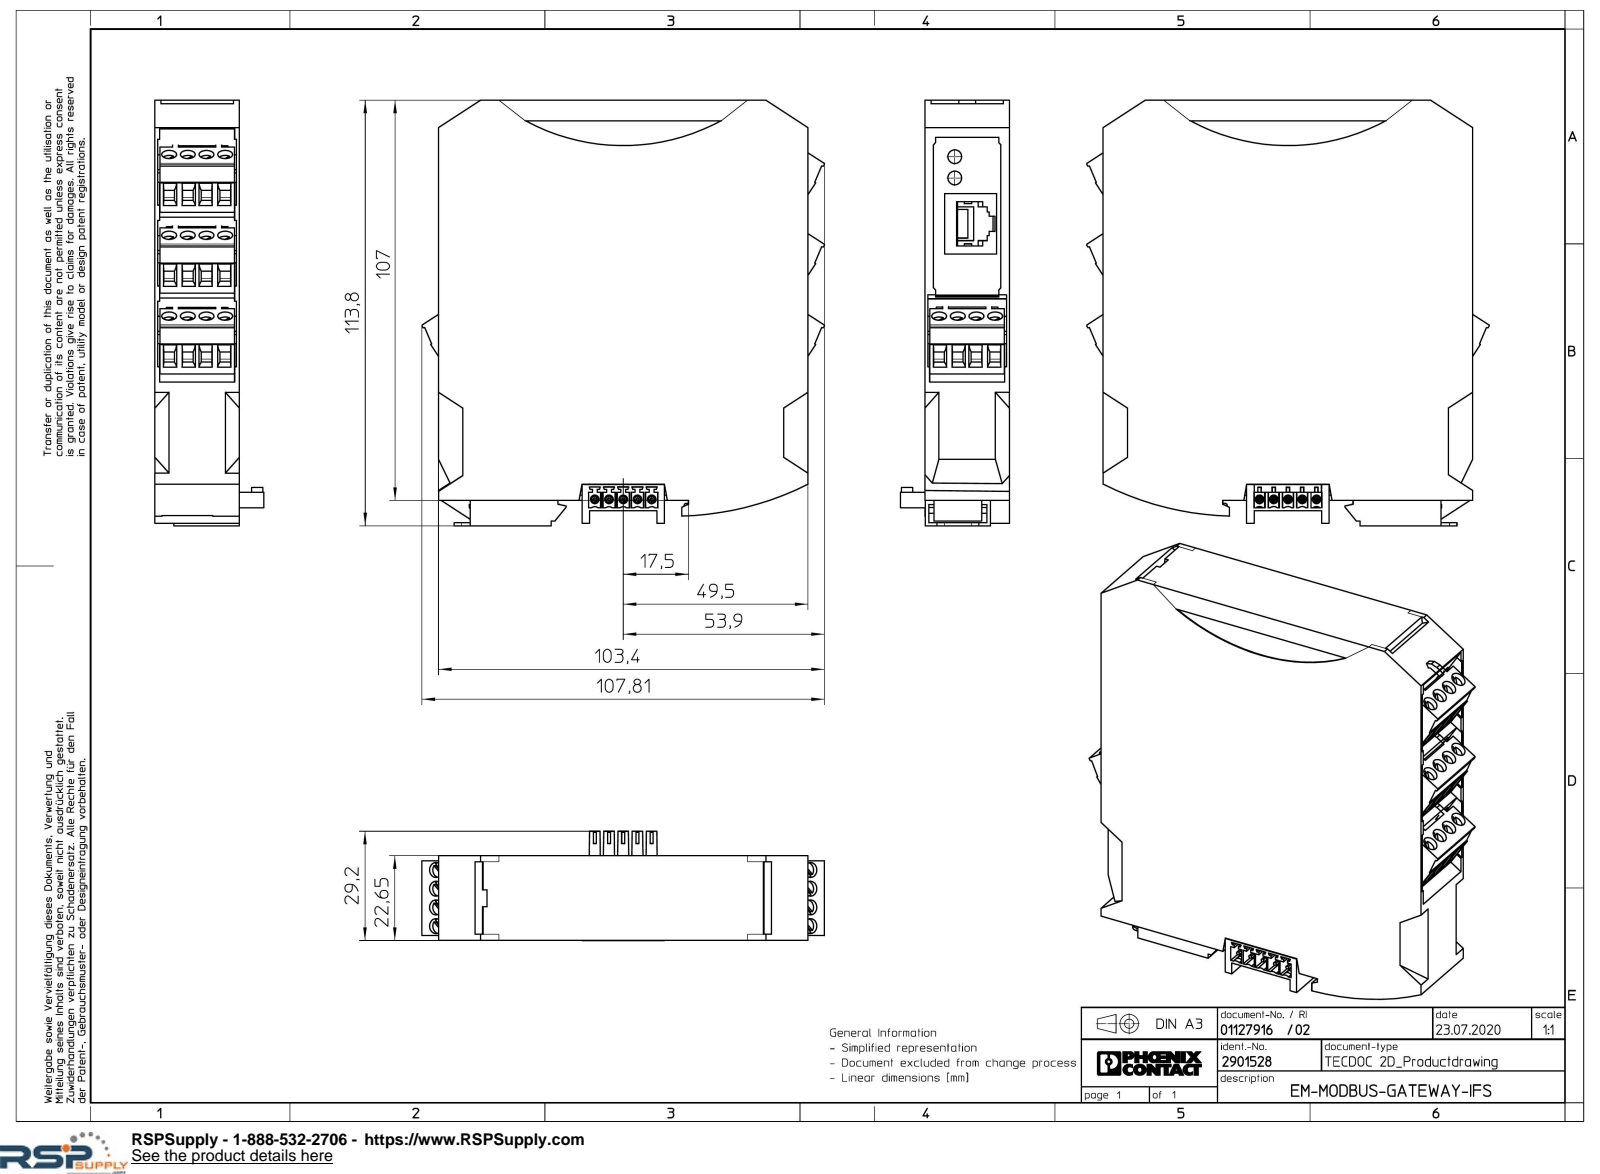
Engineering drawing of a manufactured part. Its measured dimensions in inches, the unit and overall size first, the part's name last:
Units: inches
Overall size (bounding box): 4.48 × 4.246 × 1.15
Round holes (diameter × count): ⌀0.06 ×16, ⌀0.118 ×16, ⌀0.157 ×16, ⌀0.047 ×5
Round bosses / shafts (diameter × count): ⌀0.091 ×5, ⌀0.146 ×2
Partial cylindrical surfaces — rounded edges, fillets, slot ends (radius × count): R0.079 ×34, R0.114 ×16, R0.121 ×16, R0.134 ×16, R0.016 ×6, R0.059 ×5, R0.065 ×5, R0.008 ×4
Main face-to-face distances: 0.89, 0.03, 0.86, 0.713, 0.463, 0.831, 0.838, 0.837, 0.052, 0.052
Hole centre spacings: 0.197, 0.394, 0.591, 0.503, 0.504, 0.74, 0.74, 0.947
Volume: 14.3 in³ · Surface area: 81.93 in²
Bodies: 6 solids, 1848 faces (1489 planar, 245 cylindrical, 114 other)
Part name (STEP PRODUCT): EM-MODBUS-GATEWAY-IFS-select; ME_22.5_TBUS_1.5_5-ST-3.81_GY-select; MSTBT_2.5__4-ST_GY7035-select.3; EM-MODBUS-GATEWAY-IFS-GROUP-select
STEP written by: Creo Elements/Direct Modeling 20.1A 29-Sep-2018 (C) Parametric Technology GmbH (AUTOMOTIVE_DESIGN)
